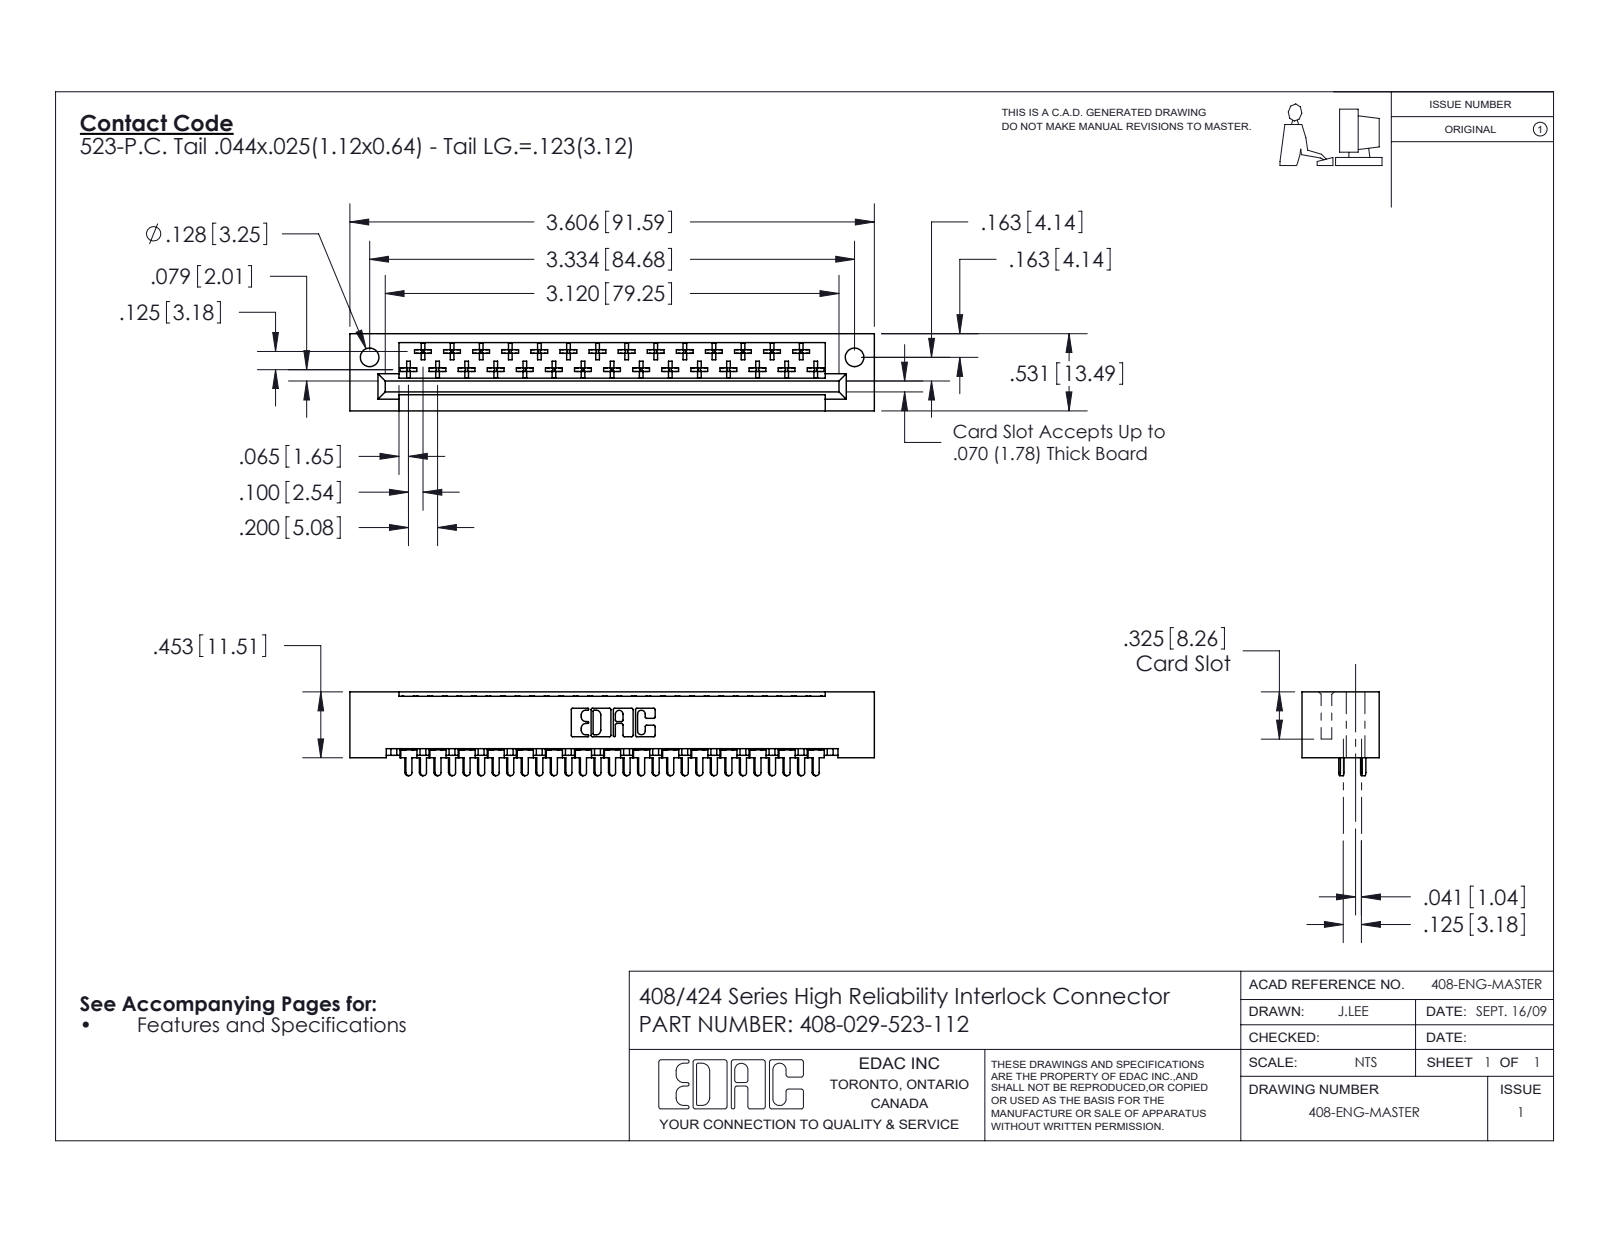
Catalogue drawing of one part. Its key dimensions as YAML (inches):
part_name: "408 Part_029 - 1; 408-290-001_408-290-123 - Top; 408-029-523-112; 408-290-001_408-290-123 - Bottom"
step_written_by: "SolidWorks 2016 (CONFIG_CONTROL_DESIGN)"
units: inches
bodies: {solids: 30, faces: 1725, planar: 1297, cylindrical: 312, other: 116}
overall_size: [3.606, 0.576, 0.531]
volume: 0.643
surface_area: 18.98
round_holes:
  - {diameter: 0.128, count: 2}
partial_cylinders:
  - {radius: 0.01, count: 174}
  - {radius: 0.02, count: 31}
  - {radius: 0.022, count: 29}
  - {radius: 0.01, count: 22}
  - {radius: 0.007, count: 6}
  - {radius: 0.031, count: 6}
  - {radius: 0.026, count: 3}
face_to_face_distances: [0.531, 0.025, 0.4, 0.1, 0.125, 0.025, 0.272, 0.235, 0.259, 0.296]
hole_center_spacings: [3.334]
